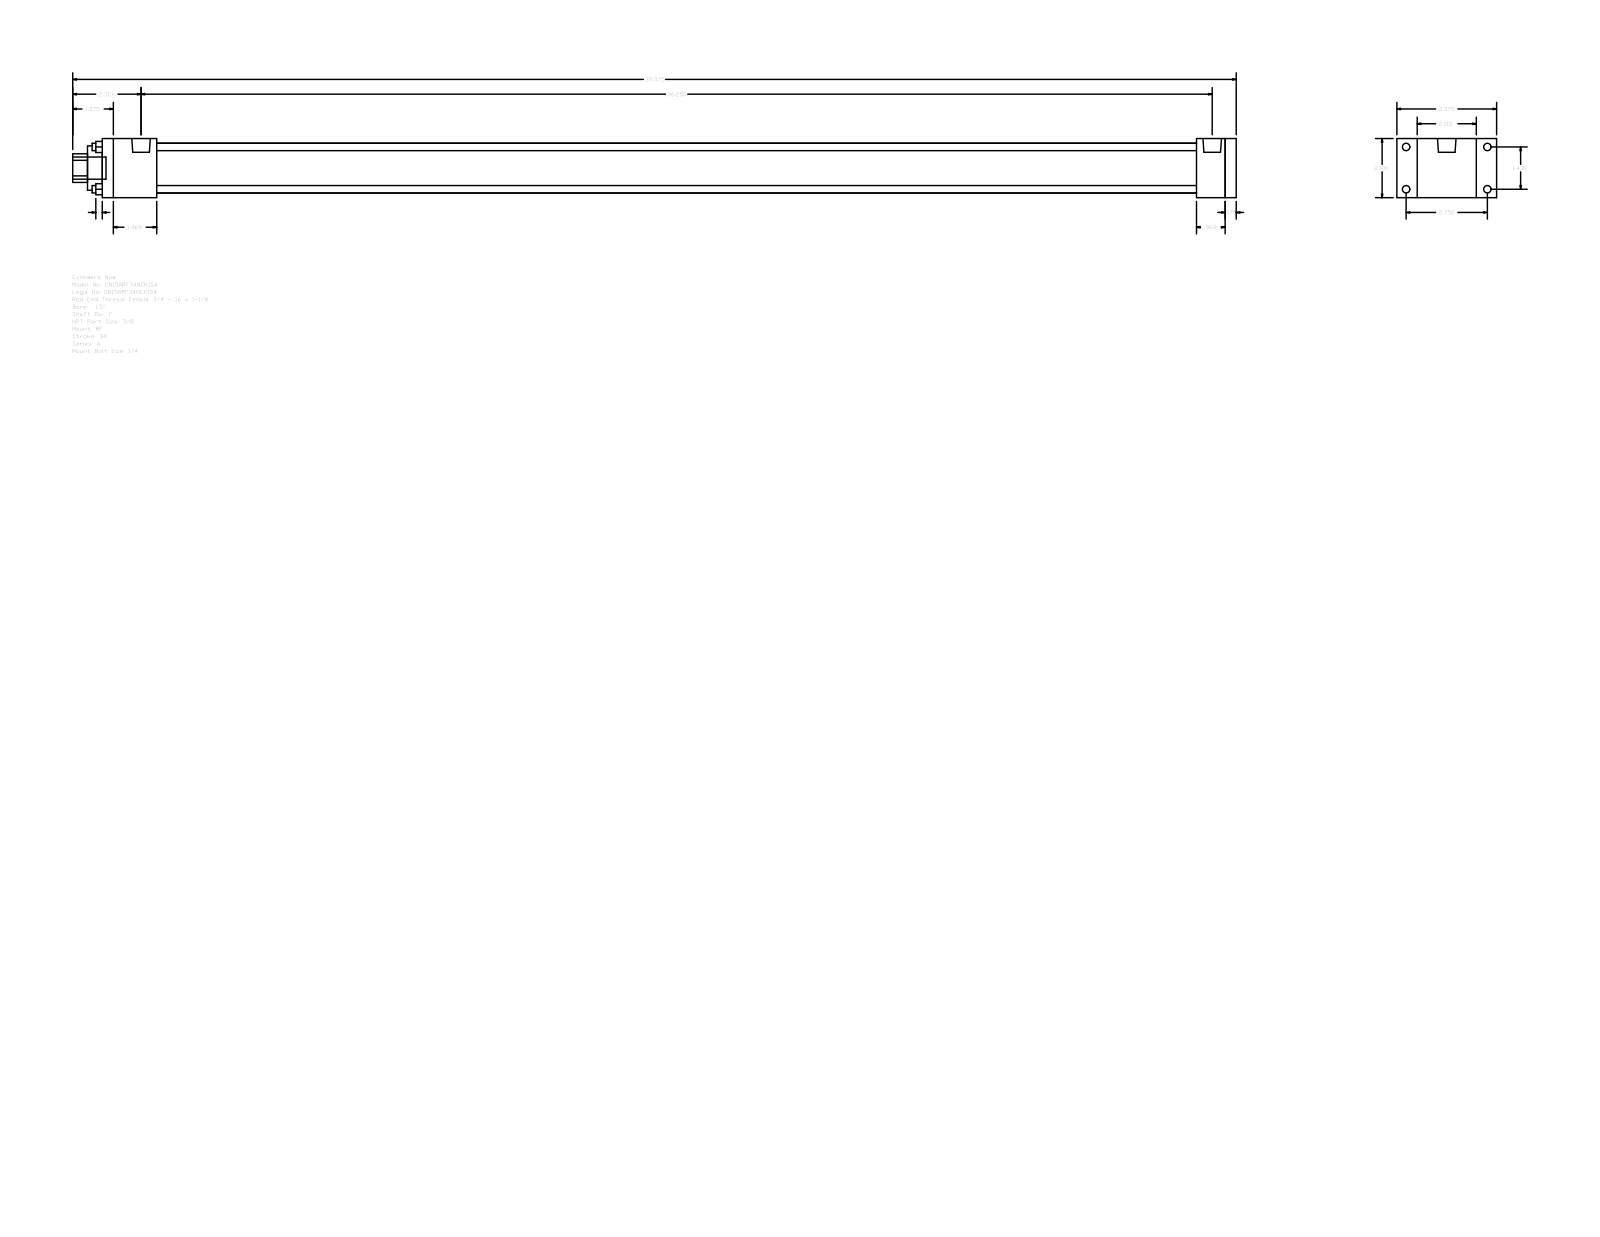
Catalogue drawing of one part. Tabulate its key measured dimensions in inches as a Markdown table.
| quantity | value |
| --- | --- |
| part name | A_RF__0150_1 |
| STEP written by | GSSL Pune (CONFIG_CONTROL_DESIGN) |
| units | inches |
| bodies | 0 solids, 92 faces (64 planar, 28 cylindrical, 0 other) |
| overall size | 39.375 × 3.375 × 2 |
| round holes (diameter × count) | 0.25 × 4, 1 × 1, 1.5 × 1, 1.69 × 1 |
| round bosses / shafts (diameter × count) | 0.25 × 4, 0.219 × 4, 0.627 × 2, 0.75 × 1 |
| partial cylindrical surfaces (radius × count) | 0.484 × 1 |
| main face-to-face distances | 2, 0.375, 38, 38.375, 37.031, 0.969, 1.344, 1.844, 35.187, 36.156 |
| hole center spacings | 1.011, 1.43, 2.022 |
